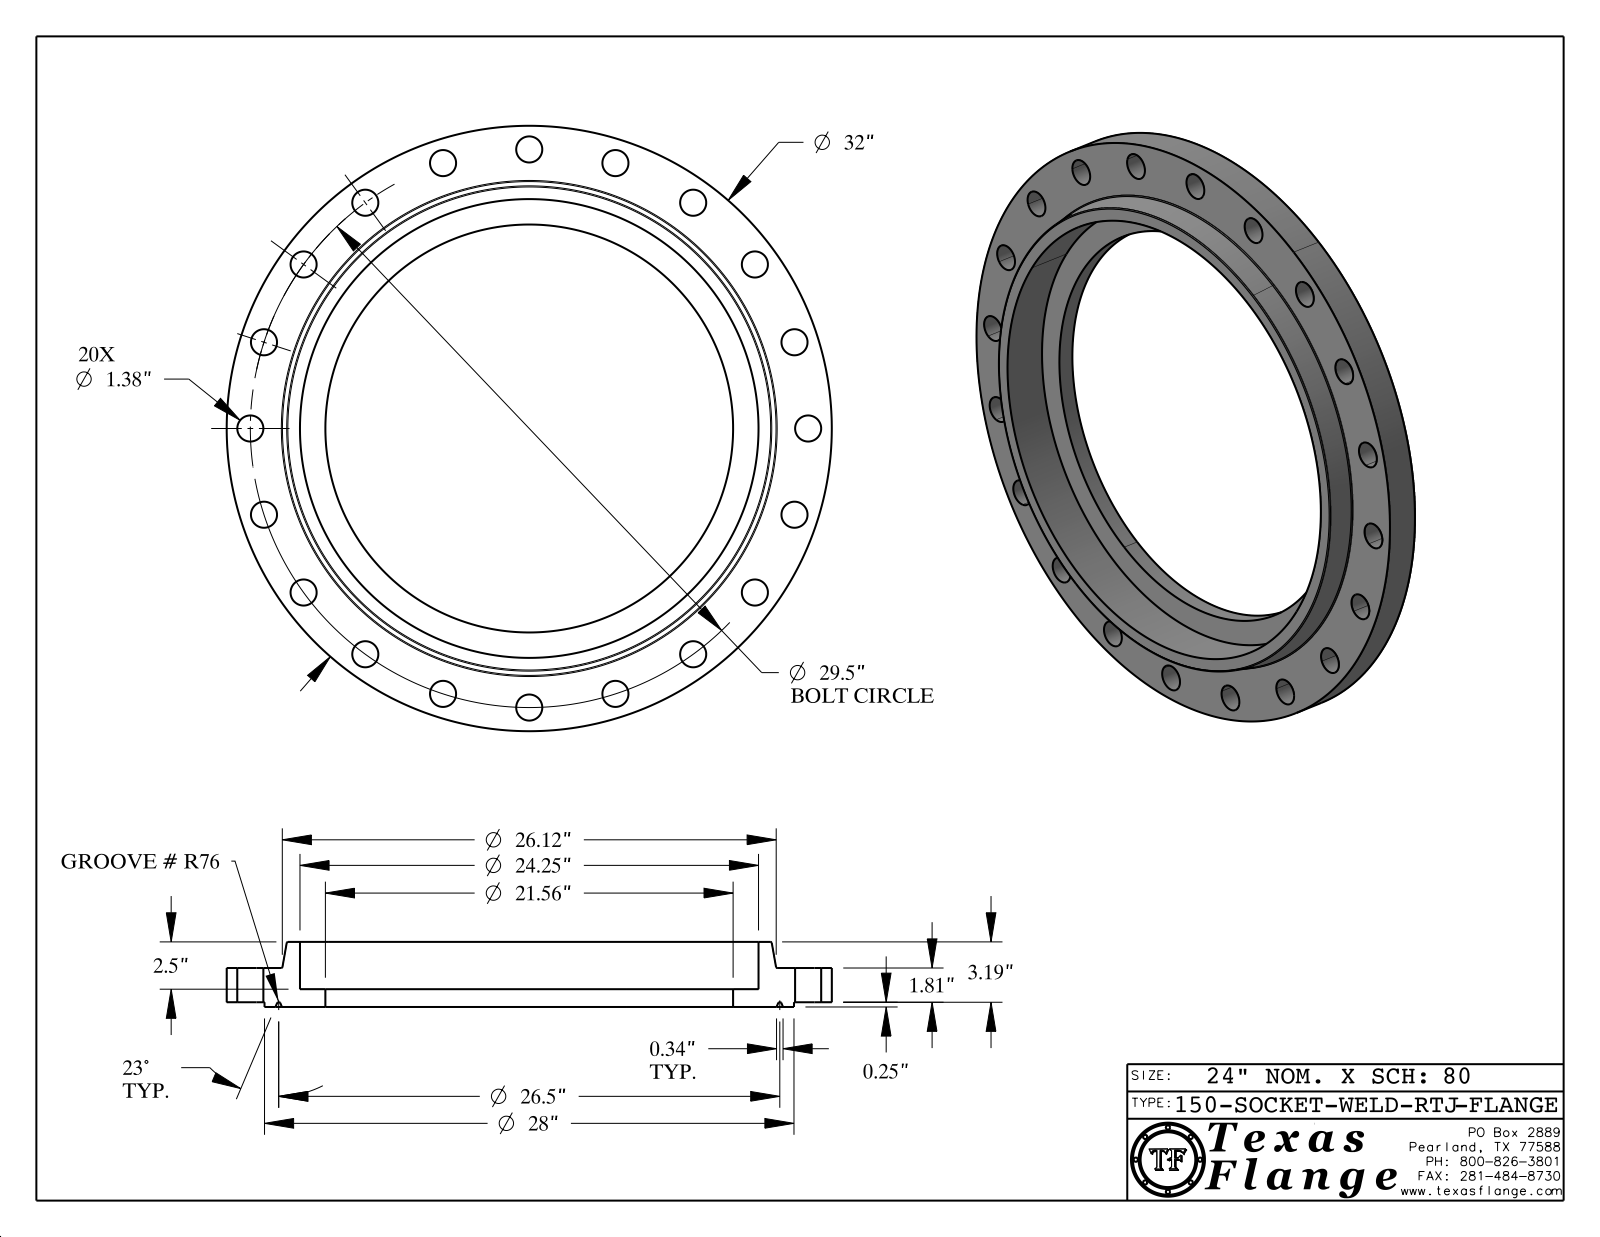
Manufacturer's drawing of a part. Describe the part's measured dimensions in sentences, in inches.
The part is named "150-SOCKET-WELD-RTJ". Its 3-D file was written by "CATIA V5 STEP AP214 (AUTOMOTIVE_DESIGN)". It is 1 solid with 454 faces: 372 planar, 68 cylindrical and 14 other. Overall it measures 32 by 32 by 3.44 inches. Its volume is 778.4 cubic inches and its surface area 1 552 square inches. Round holes: 20 of diameter 1.38, 1 of diameter 0.495, 1 of diameter 21.562, 1 of diameter 24.25. Round bosses or shafts: 8 of diameter 0.03, 1 of diameter 32, 1 of diameter 28, 1 of diameter 0.39. The main face-to-face distances are 2.06, 0.25, 1.81, 0.94, 0.69, 1.12, 3.44, 3.19, 2.5, 1.38. The hole center spacings are 14.75, 29.137, 4.615, 17.34, 20.859, 23.866, 26.285, 9.116.
